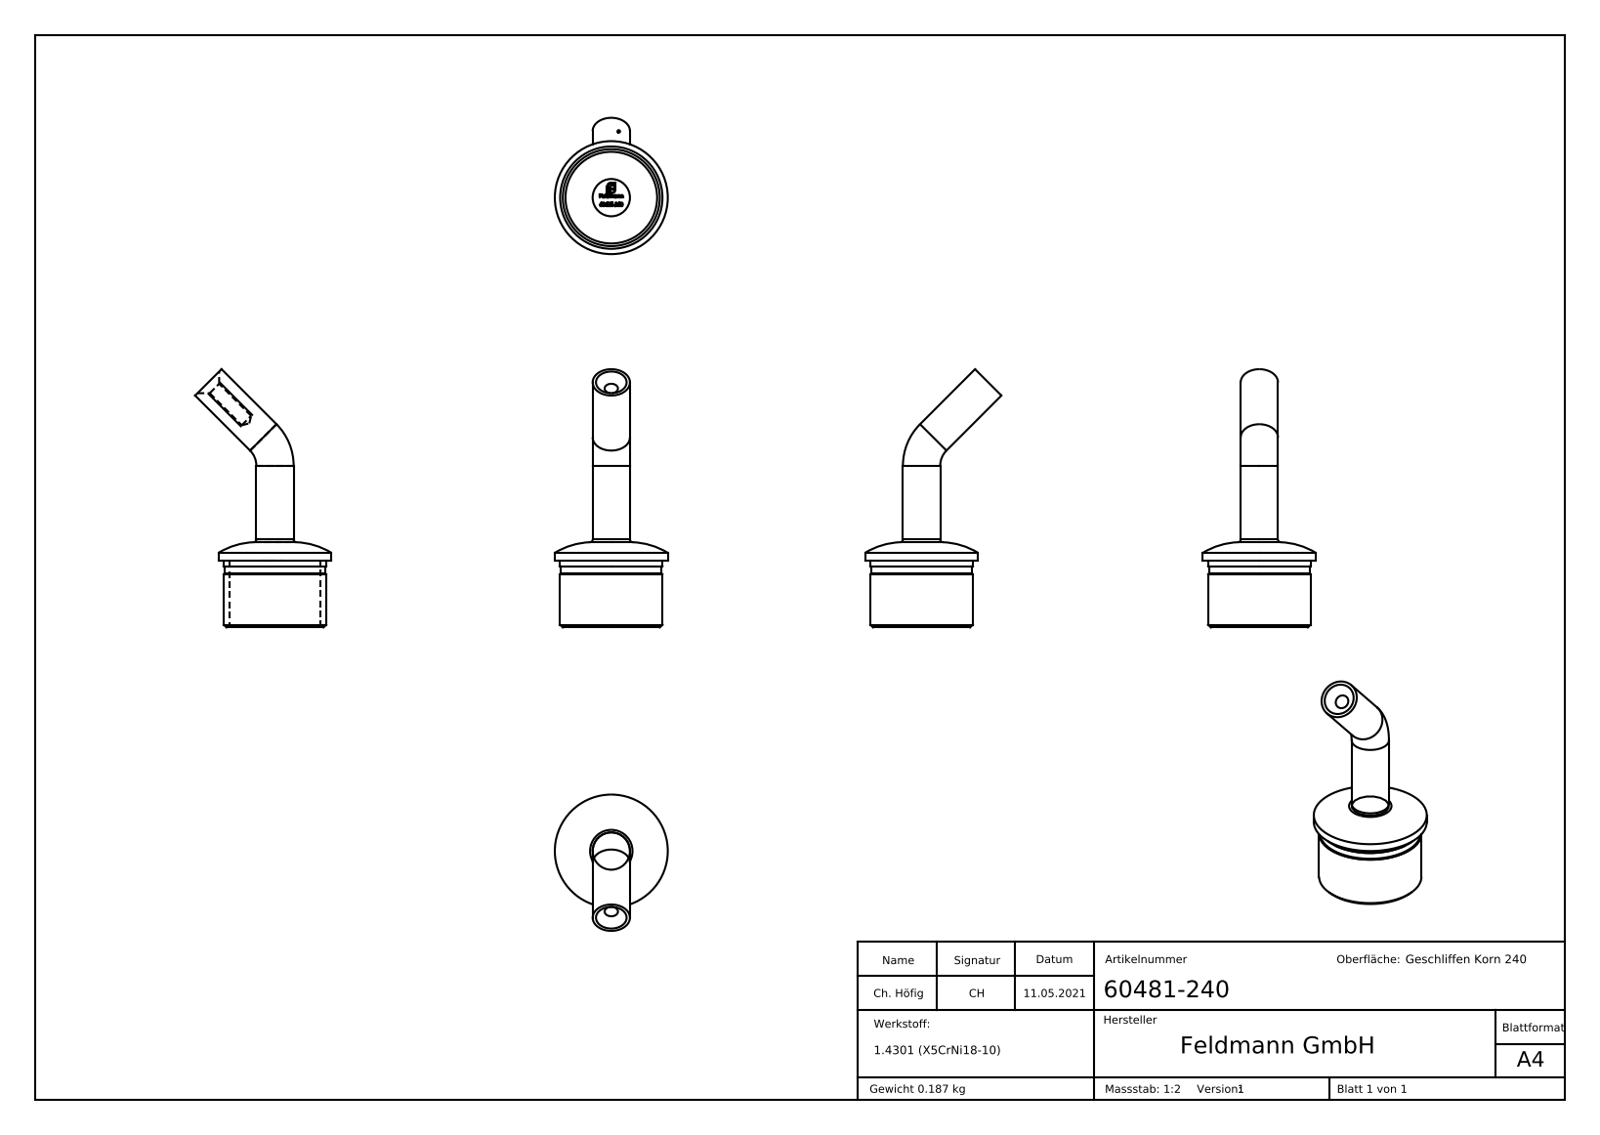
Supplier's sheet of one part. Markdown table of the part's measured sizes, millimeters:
| quantity | value |
| --- | --- |
| part name | 60481-240 |
| STEP written by | SolidWorks 2018 (CONFIG_CONTROL_DESIGN) |
| units | millimeters |
| bodies | 1 solid, 296 faces (154 planar, 16 cylindrical, 126 other) |
| overall size | 96.95 × 51.17 × 42.4 |
| volume | 23 615 mm³ |
| surface area | 12 350 mm² |
| round holes (diameter × count) | 5 × 1, 34.4 × 1 |
| round bosses / shafts (diameter × count) | 14 × 2, 42.4 × 1, 38.4 × 1, 37.8 × 1 |
| main face-to-face distances | 25, 25.1, 3, 2.1, 20, 5, 5.1, 23, 2, 0.31 |
